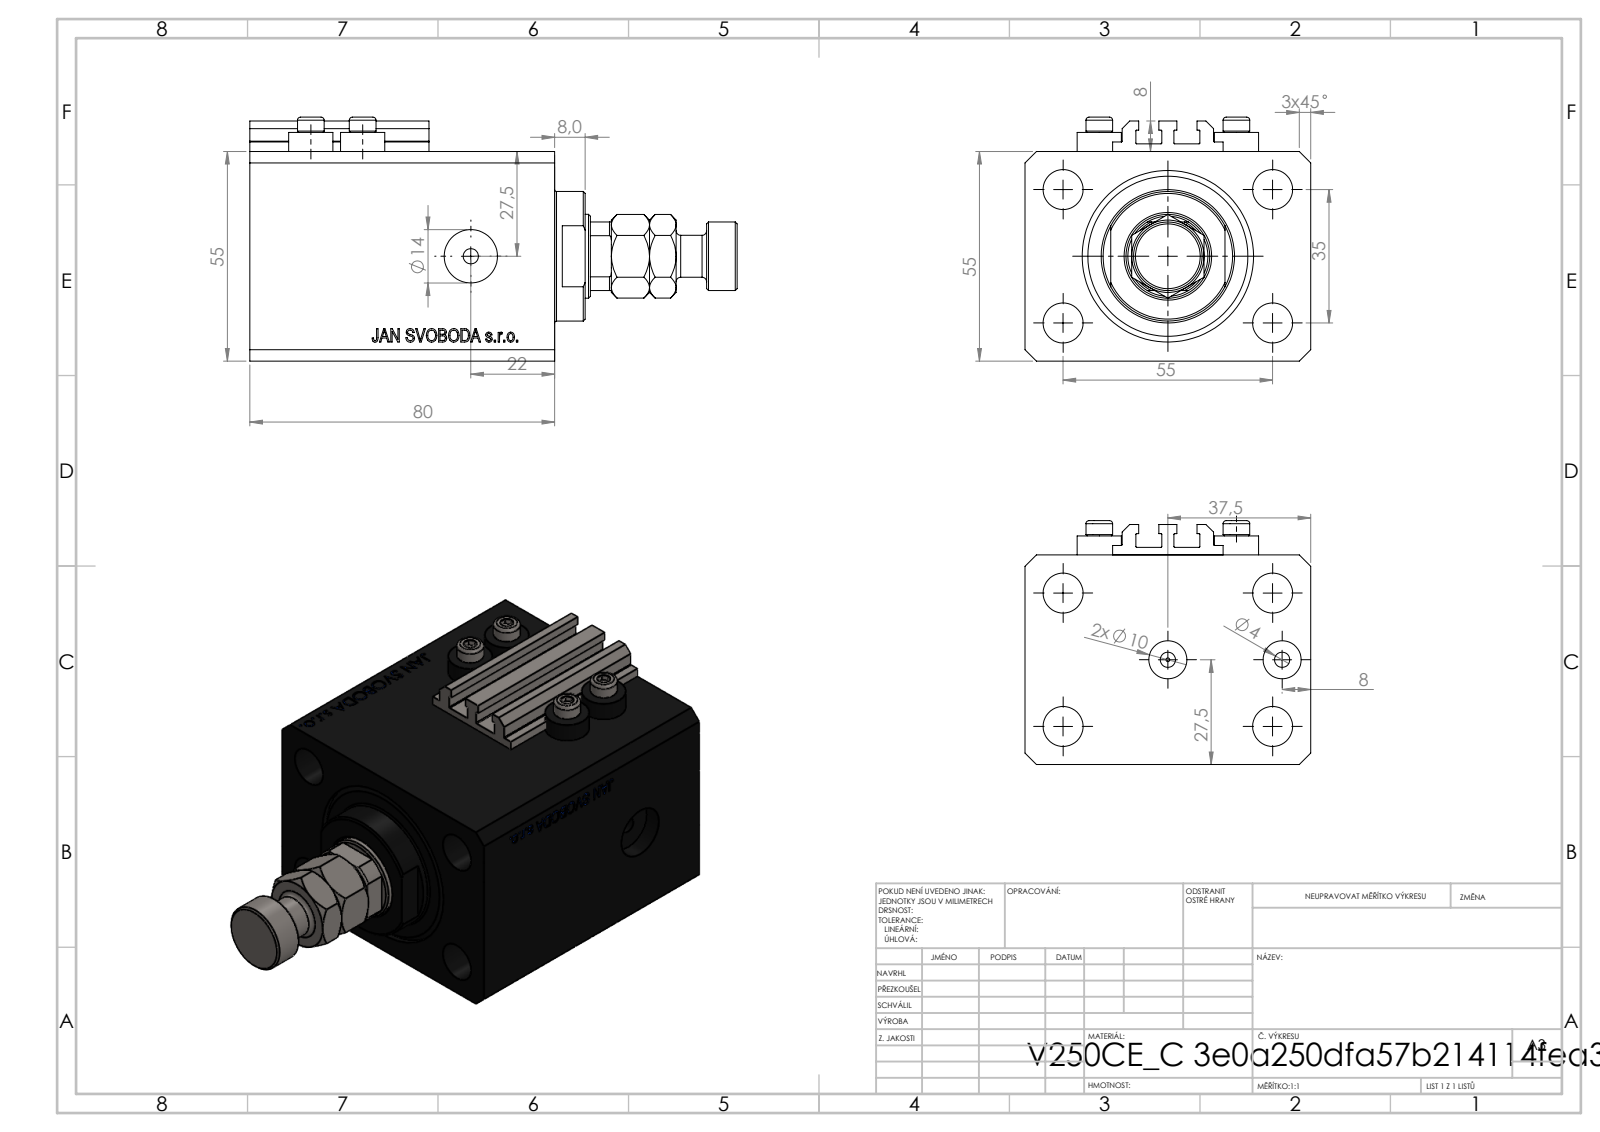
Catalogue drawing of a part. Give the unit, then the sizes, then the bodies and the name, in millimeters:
Units: millimetres
Overall size (bounding box): 127.9 × 75 × 64
Round holes (diameter × count): ⌀4 ×8, ⌀10.5 ×5, ⌀10 ×2, ⌀14 ×2, ⌀1.25 ×1, ⌀22 ×1, ⌀32 ×1, ⌀45 ×1
Round bosses / shafts (diameter × count): ⌀11.6 ×4, ⌀7 ×4, ⌀34 ×1, ⌀18 ×1, ⌀11 ×1
Partial cylindrical surfaces — rounded edges, fillets, slot ends (radius × count): R0.2 ×10, R10.5 ×1
Main face-to-face distances: 55, 75, 80, 52.9, 27.1, 43, 9.9, 70.1, 8, 3
Hole centre spacings: 32.6, 36, 13.6, 17.68, 35, 38.48, 55, 60.1
Volume: 312 720 mm³ · Surface area: 77 152 mm²
Bodies: 9 solids, 1094 faces (520 planar, 96 cylindrical, 478 other)
Part name (STEP PRODUCT): MFA; ALLEN BOLT V250CE; V250CE_C_VCP; V250CE_C_Body (+1 more)
STEP written by: SolidWorks 2019 (CONFIG_CONTROL_DESIGN)
